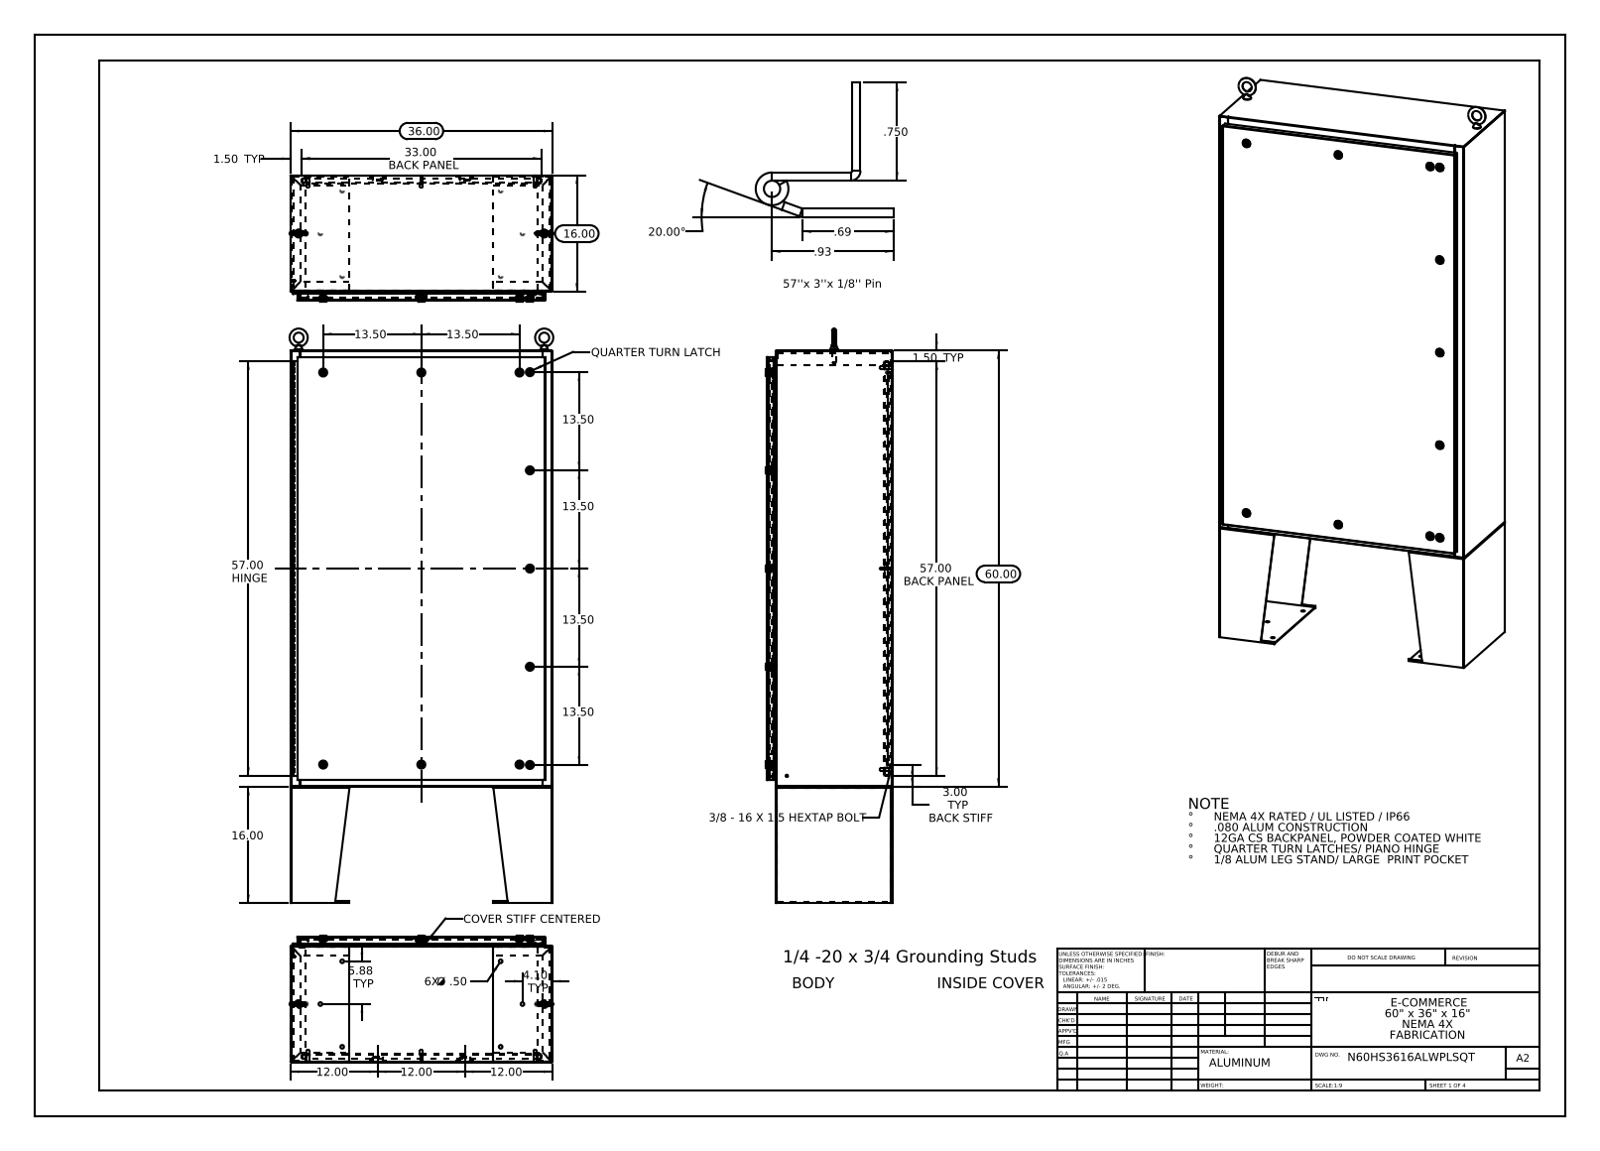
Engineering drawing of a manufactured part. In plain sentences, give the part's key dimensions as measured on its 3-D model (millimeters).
The part is named "10_30 CD Stud; N60HS3616SSWPLSQT SD-LSK-Stand; N60HS3616SSWPLSQT Backpanel; N60HS3616SSWPLSQT Door Stiffener (+8 more)". Its 3-D file was written by "SolidWorks 2013 (CONFIG_CONTROL_DESIGN)". It is 36 solids with 2369 faces: 1193 planar, 980 cylindrical and 196 other. Overall it measures 2006.6 by 921.3 by 436.9 millimeters. Its volume is 16 330 000 cubic millimeters and its surface area 15 500 000 square millimeters. Round holes: 14 of diameter 12.7, 8 of diameter 6.4, 4 of diameter 19.1, 1 of diameter 3.2, 1 of diameter 3.2. Round bosses or shafts: 10 of diameter 15.9, 8 of diameter 9.5, 8 of diameter 8.4, 8 of diameter 4, 8 of diameter 3.6, 2 of diameter 8, 2 of diameter 6, 1 of diameter 6.4. Partial cylindrical surfaces (rounded edges, fillets, slot ends): 36 of radius 0.3, 30 of radius 2.2, 11 of radius 11.2, 8 of radius 1, 8 of radius 3.6, 6 of radius 0.5, 4 of radius 3, 4 of radius 3.2. The main face-to-face distances are 1.9, 435, 2.6, 433.1, 27.3, 436.9, 912.5, 409.6, 25.4, 407.7. The hole center spacings are 56.5, 213.2, 647.2, 701.7, 721.3, 1059.4, 1458.4, 440.2.
